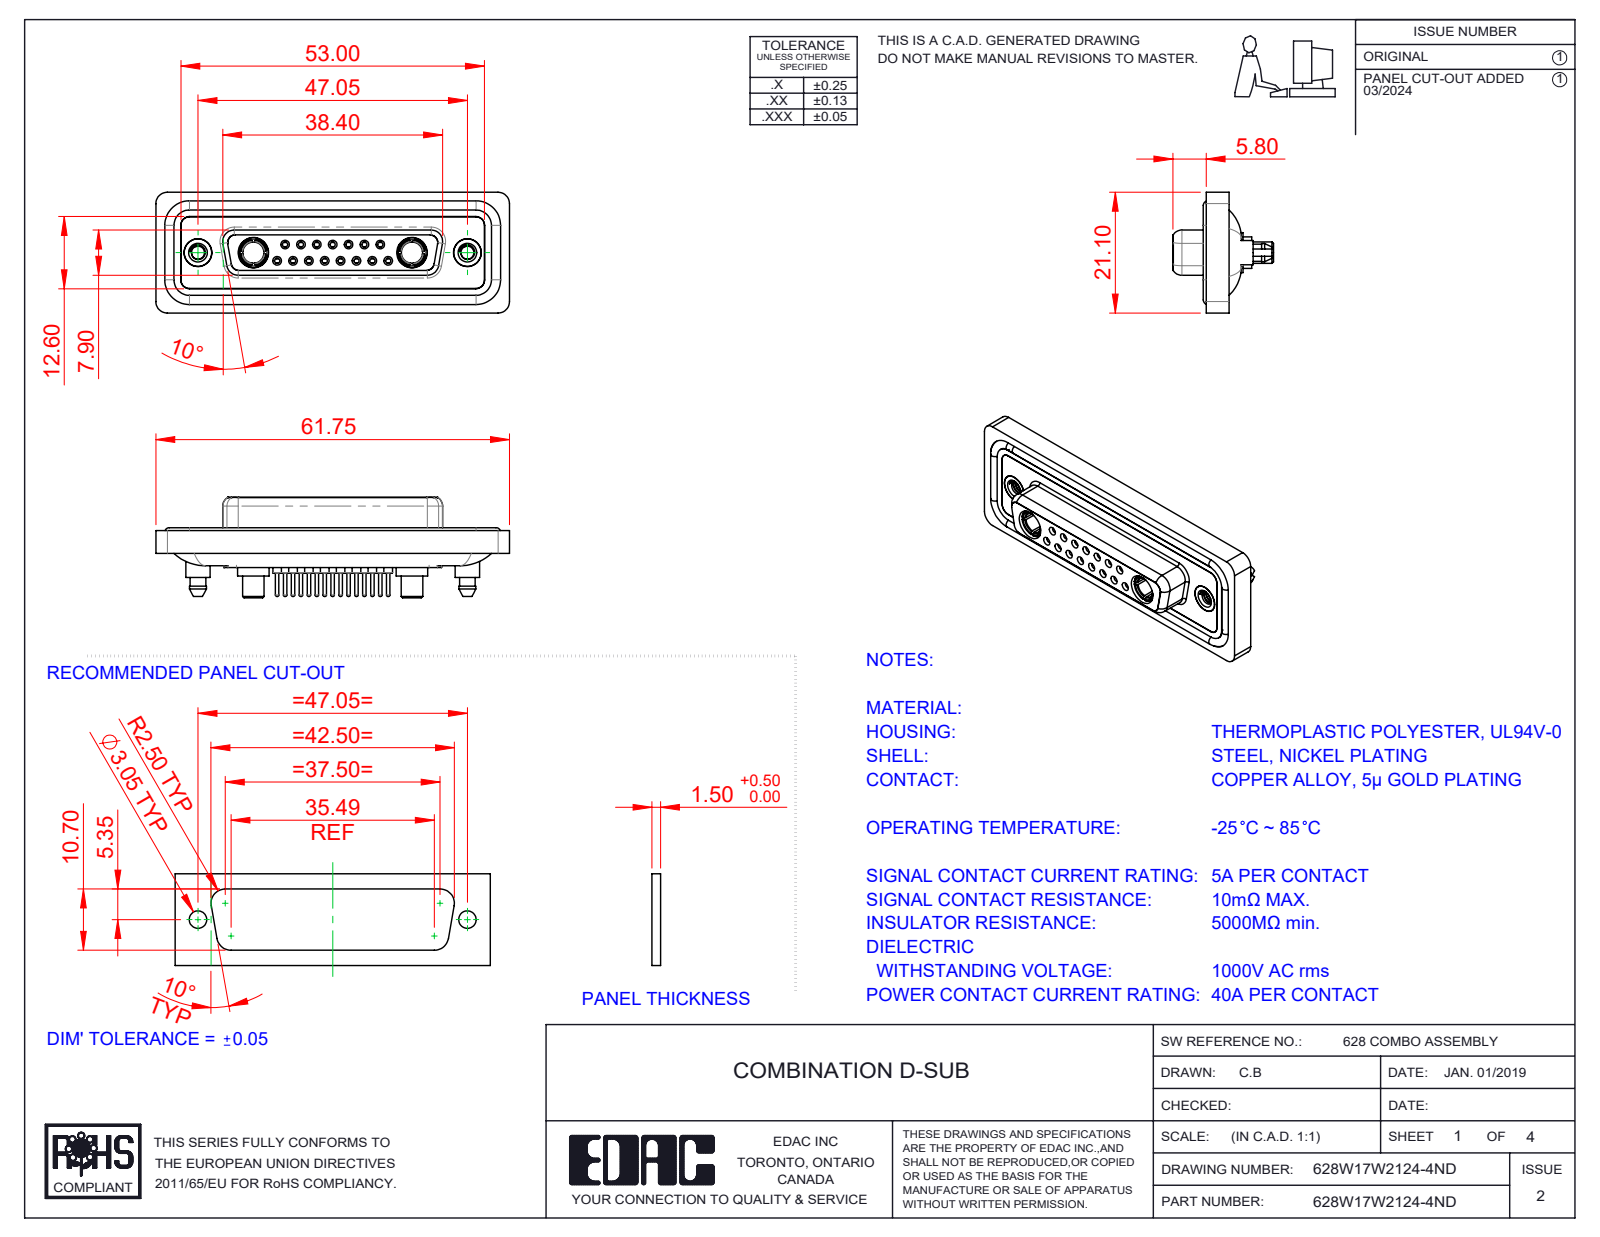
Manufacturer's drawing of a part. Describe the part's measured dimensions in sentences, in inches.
The part is named "Power Socket_40A S; 628Combo Shell Rear_25 Contacts; 628Combo Contact Row 2_24; 628Combo Threaded Boardlock_D (+5 more)". Its 3-D file was written by "SolidWorks 2023 (CONFIG_CONTROL_DESIGN)". It is 26 solids with 1425 faces: 404 planar, 567 cylindrical and 454 other. Overall it measures 2.431 by 0.831 by 0.691 inches. Its volume is 0.518 cubic inches and its surface area 22.03 square inches. Round holes: 15 of diameter 0.035, 15 of diameter 0.043, 15 of diameter 0.059, 15 of diameter 0.079, 8 of diameter 0.063, 7 of diameter 0.067, 4 of diameter 0.191, 2 of diameter 0.089, 2 of diameter 0.146, 2 of diameter 0.157, 2 of diameter 0.159, 2 of diameter 0.197. Round bosses or shafts: 15 of diameter 0.087, 15 of diameter 0.024, 11 of diameter 0.063, 2 of diameter 0.217, 2 of diameter 0.213, 2 of diameter 0.205, 2 of diameter 0.195, 2 of diameter 0.195. Partial cylindrical surfaces (rounded edges, fillets, slot ends): 24 of radius 0.059, 18 of radius 0.079, 10 of radius 0.063, 8 of radius 0.053, 4 of radius 0.01, 4 of radius 0.02, 4 of radius 0.024, 4 of radius 0.026. The main face-to-face distances are 0.016, 0.071, 0.293, 0.222, 0.26, 0.02, 0.278, 0.063, 0.114, 0.043. The hole center spacings are 0.124, 0.109, 0.327, 0.218, 0.198, 0.198, 0.295, 0.436.
